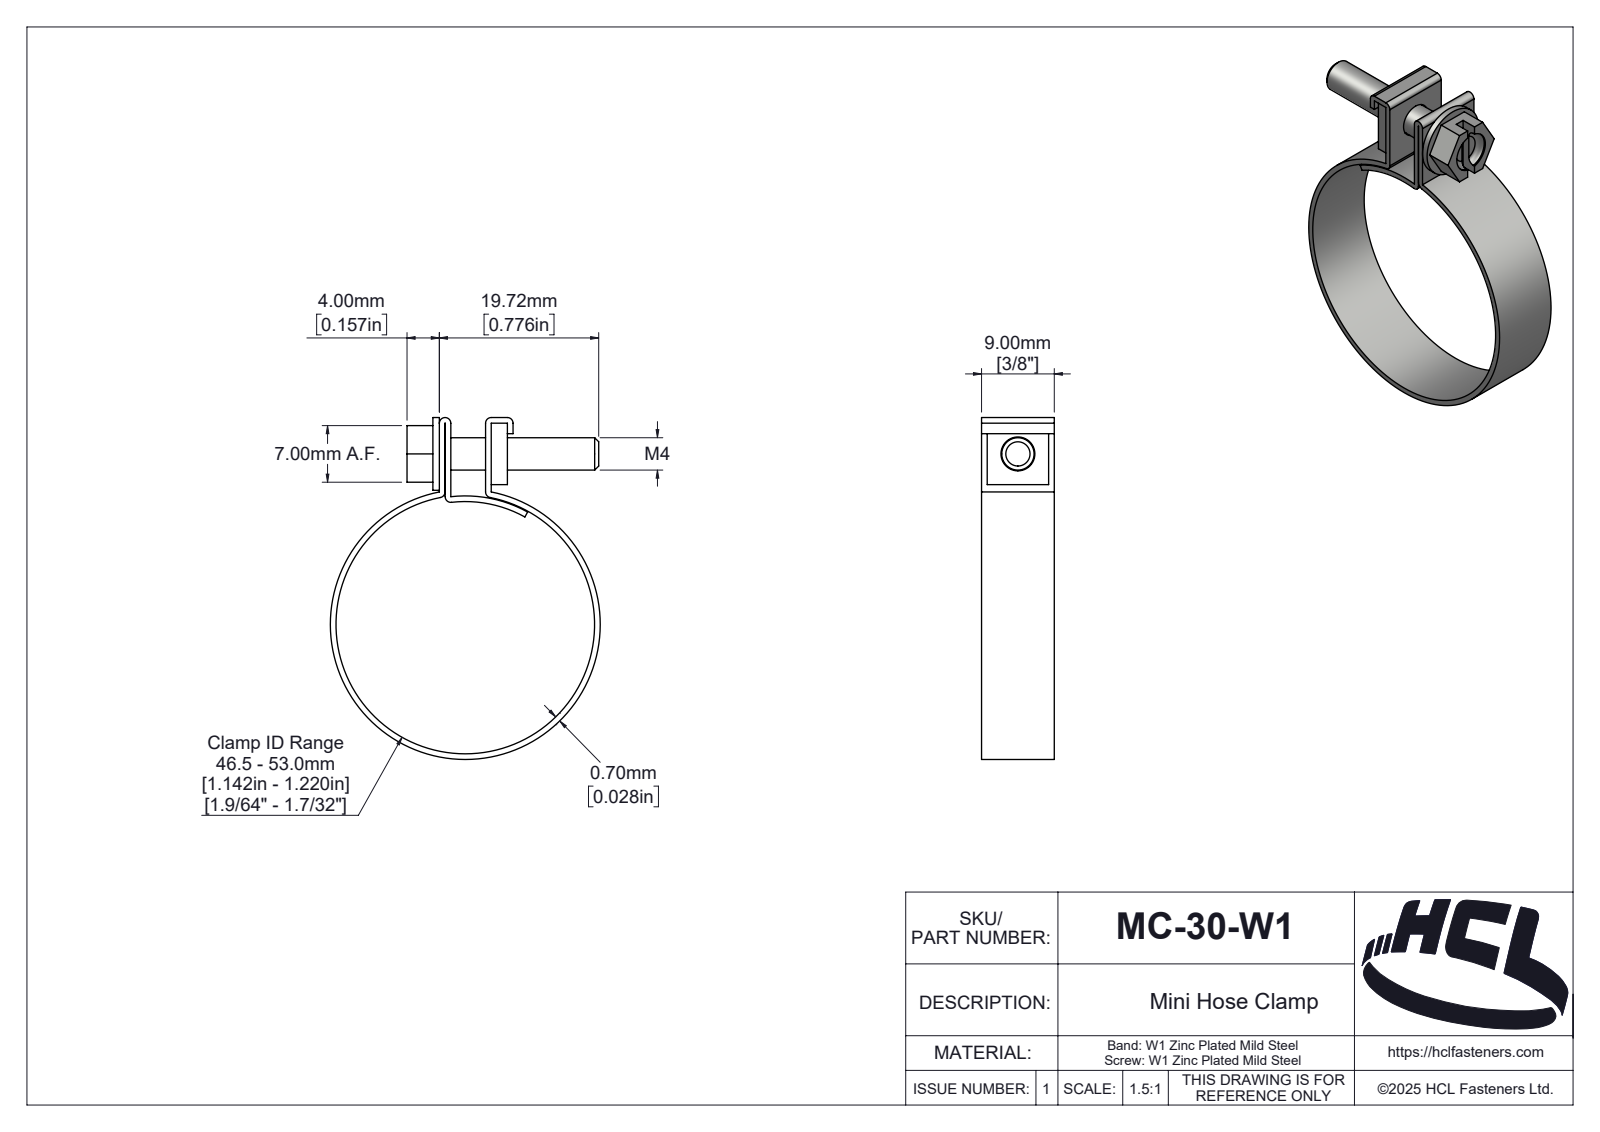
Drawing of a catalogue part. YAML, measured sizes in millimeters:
part_name: "MC-30-W1"
step_written_by: "SolidWorks 2025 (AUTOMOTIVE_DESIGN)"
units: millimeters
bodies: {solids: 3, faces: 170, planar: 38, cylindrical: 79, other: 53}
overall_size: [42.29, 33.4, 9]
volume: 1339
surface_area: 3330
round_holes:
  - {diameter: 4.2, count: 1}
  - {diameter: 5, count: 1}
  - {diameter: 32, count: 1}
round_bosses_or_shafts:
  - {diameter: 33.4, count: 1}
  - {diameter: 9, count: 1}
  - {diameter: 4, count: 1}
partial_cylinders:
  - {radius: 0.7, count: 5}
  - {radius: 0.2, count: 1}
  - {radius: 0.71, count: 1}
  - {radius: 0.81, count: 1}
  - {radius: 1.01, count: 1}
  - {radius: 1.06, count: 1}
  - {radius: 1.28, count: 1}
  - {radius: 1.81, count: 1}
face_to_face_distances: [0.7, 5, 0.72, 5.72, 6.42, 9, 7, 2, 2.7, 8.42]
